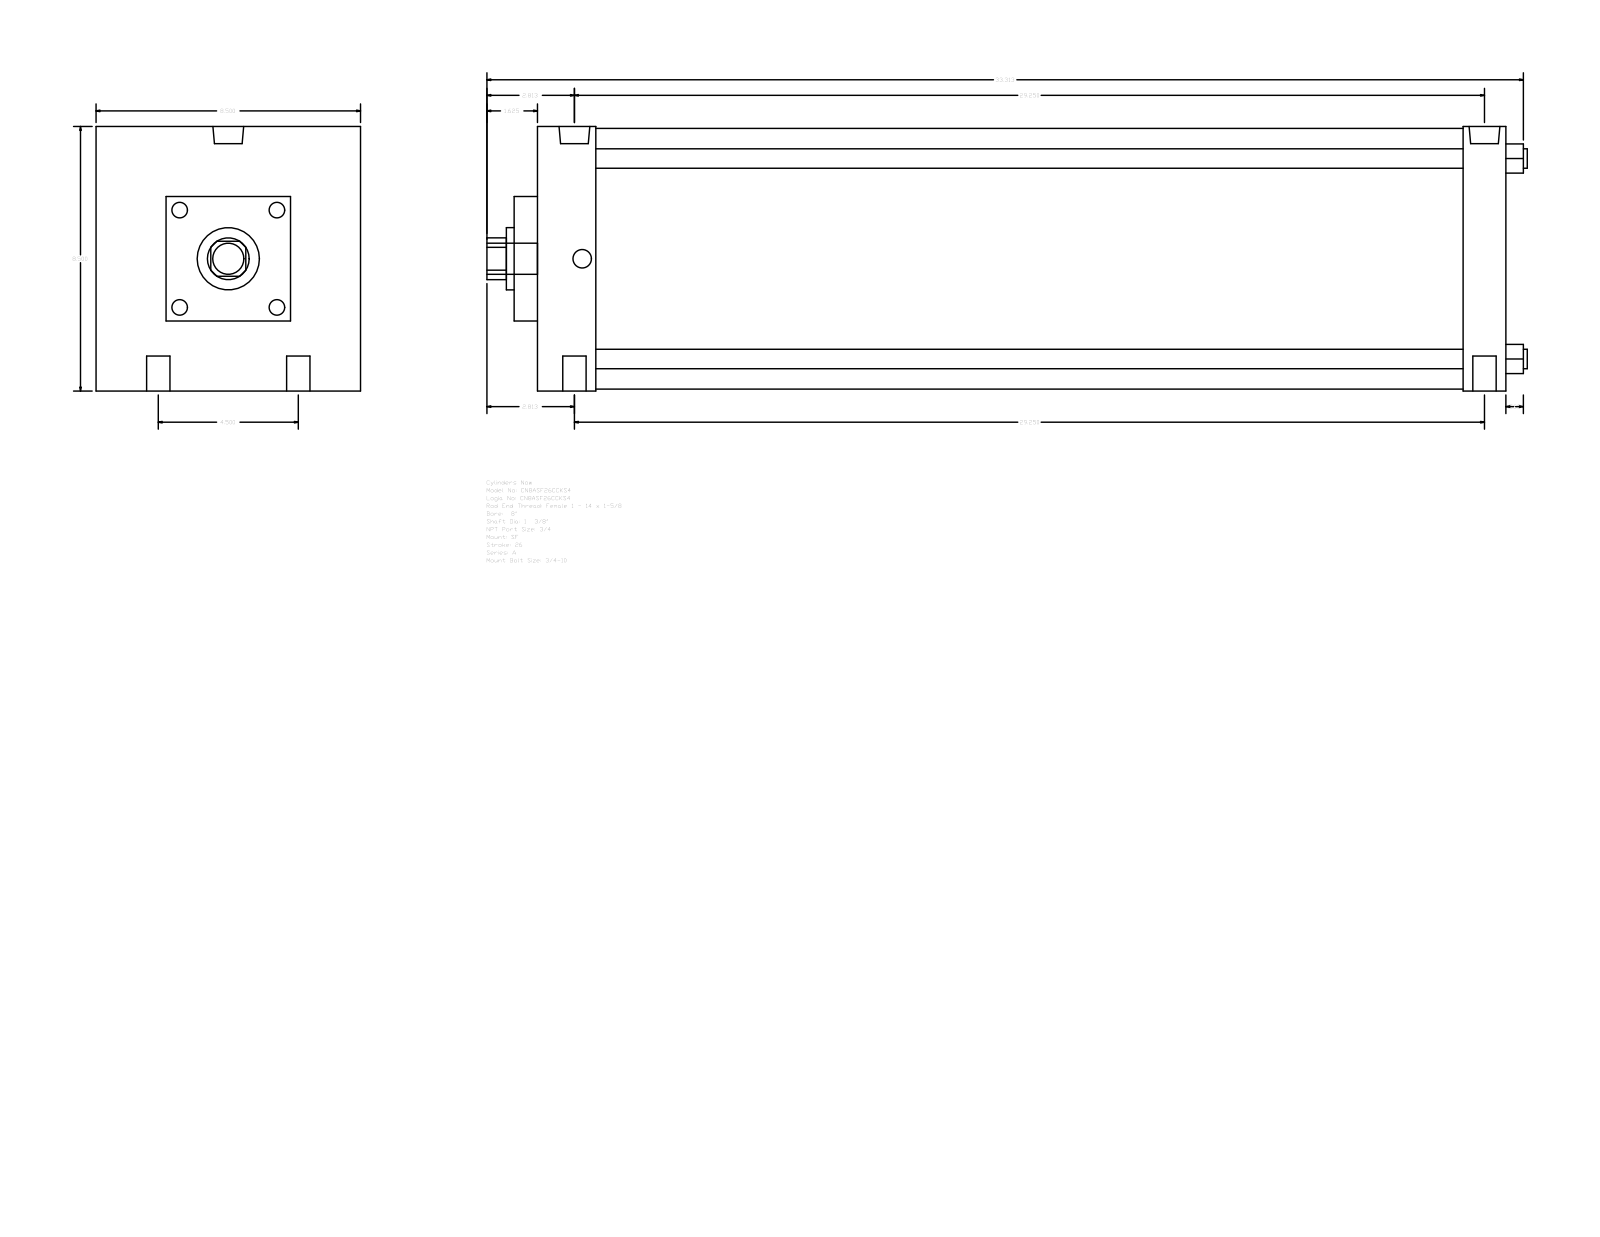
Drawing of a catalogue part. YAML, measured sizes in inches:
part_name: "A_SF__0800_1.375"
step_written_by: "GSSL Pune (CONFIG_CONTROL_DESIGN)"
units: inches
bodies: {solids: 0, faces: 93, planar: 67, cylindrical: 26, other: 0}
overall_size: [33.437, 8.5, 8.5]
round_holes:
  - {diameter: 0.75, count: 4}
  - {diameter: 0.594, count: 2}
  - {diameter: 0.989, count: 2}
  - {diameter: 1.375, count: 1}
  - {diameter: 2, count: 1}
round_bosses_or_shafts:
  - {diameter: 0.625, count: 4}
  - {diameter: 8.375, count: 1}
  - {diameter: 1, count: 1}
partial_cylinders:
  - {radius: 0.672, count: 1}
face_to_face_distances: [31.125, 8.5, 1.875, 29.75, 27.875, 29.25, 1.375, 0.75, 2.625, 30.5]
hole_center_spacings: [2.25, 29.336, 29.25, 4.5, 29.594, 28.75]
